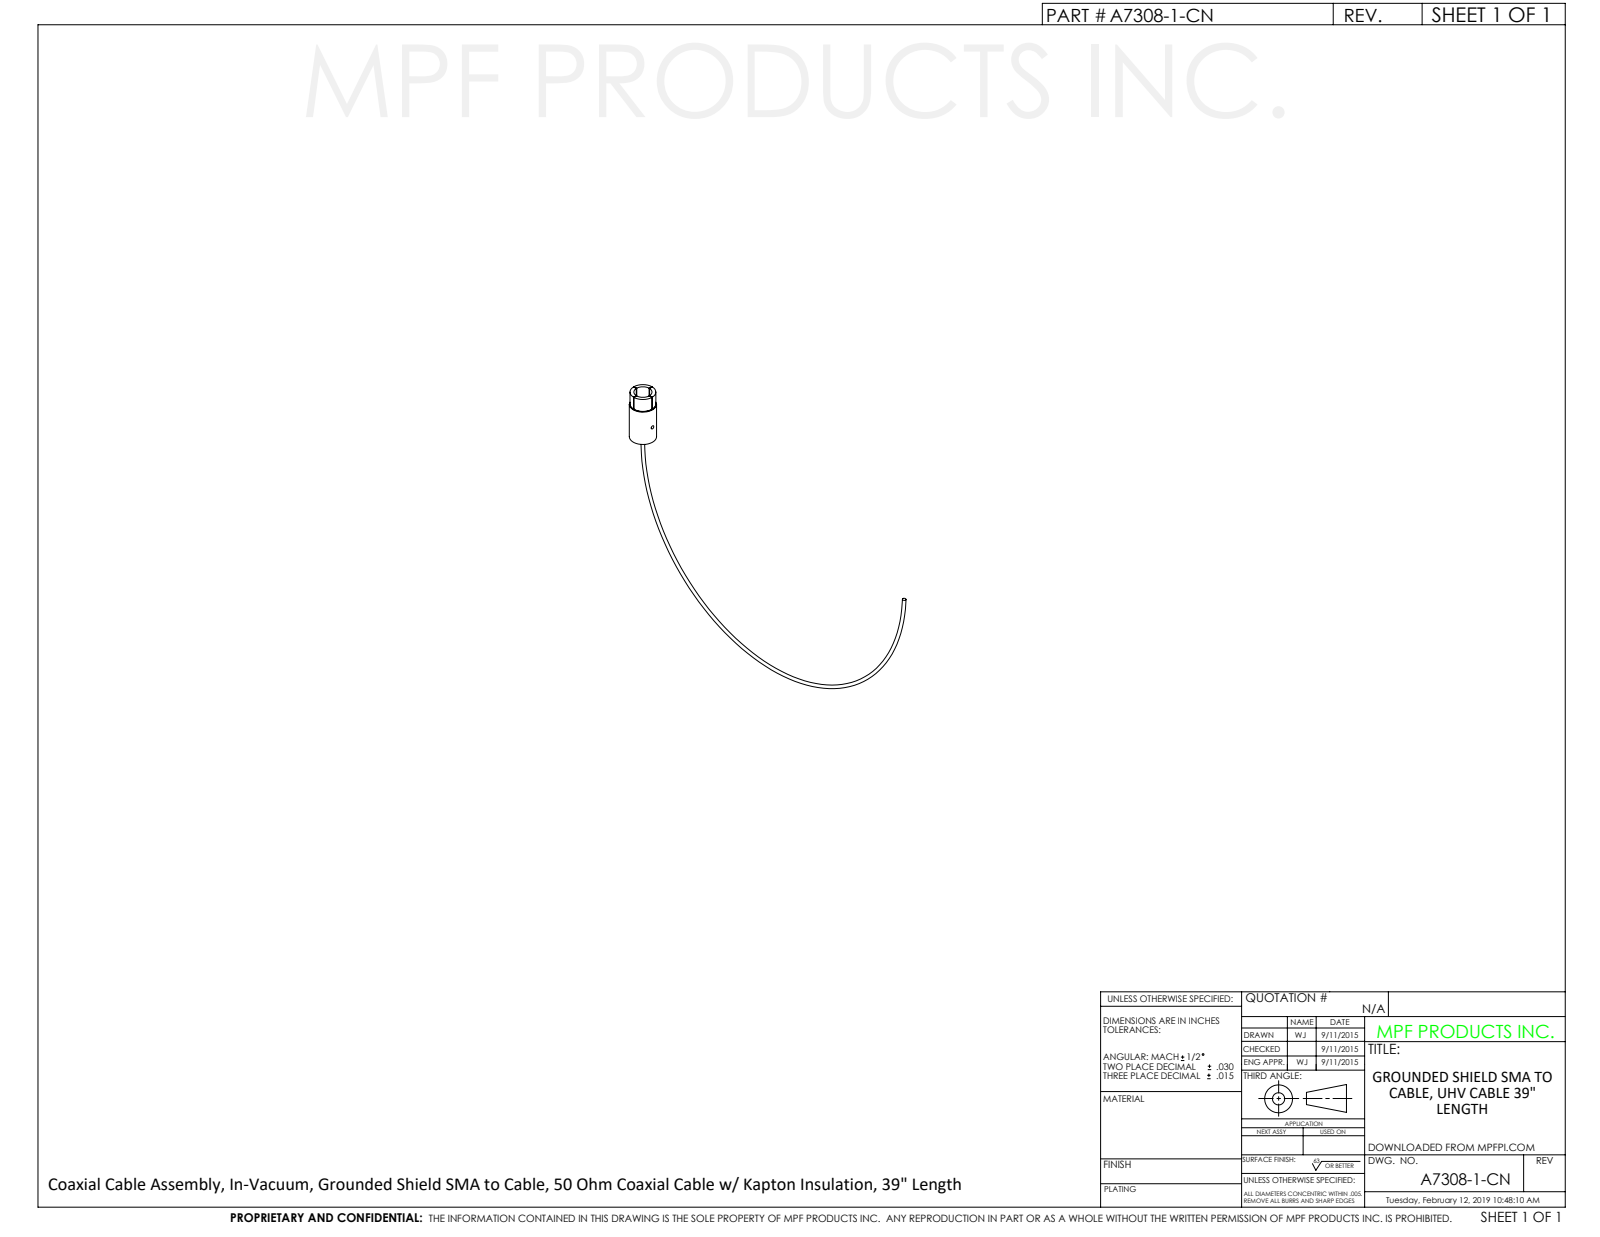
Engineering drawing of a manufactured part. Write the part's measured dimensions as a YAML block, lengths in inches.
part_name: "A7307-1-CN"
step_written_by: "SolidWorks 2012 (CONFIG_CONTROL_DESIGN)"
units: inches
bodies: {solids: 1, faces: 34, planar: 17, cylindrical: 12, other: 5}
overall_size: [10.587, 6.833, 0.75]
volume: 0.509
surface_area: 11.78
round_holes:
  - {diameter: 0.1, count: 2}
  - {diameter: 0.5, count: 1}
round_bosses_or_shafts:
  - {diameter: 0.75, count: 1}
  - {diameter: 0.71, count: 1}
face_to_face_distances: [1.5, 0.2, 1.3, 0.02, 1.1, 0.9, 0.4]
